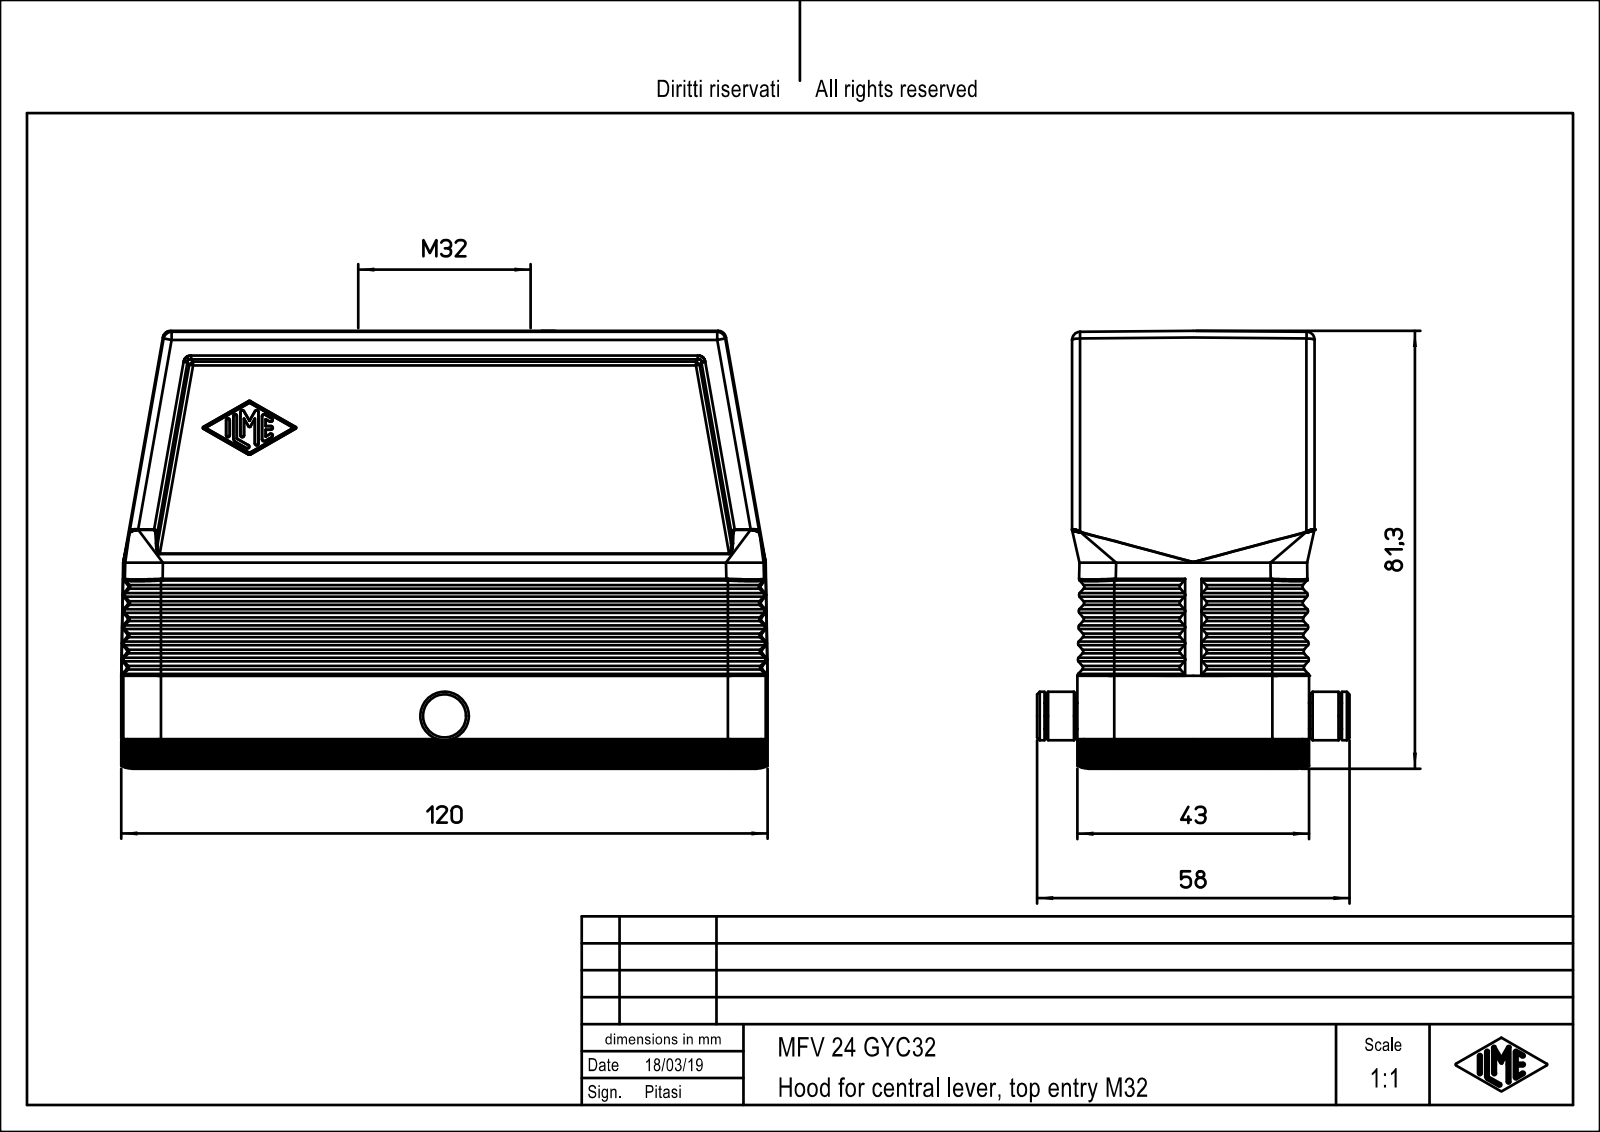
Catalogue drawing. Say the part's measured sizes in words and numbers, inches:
The part is named "MFV_24_GYC32". Its 3-D file was written by "PTC Creo Elements/Direct Modeling 19.0E 27-Jun-2016 (C) Parametric Technology GmbH (AUTOMOTIVE_DESIGN)". It is 1 solid with 574 faces: 224 planar, 182 cylindrical and 168 other. Overall it measures 4.724 by 3.199 by 2.283 inches. Its volume is 7.583 cubic inches and its surface area 90.57 square inches. Round holes: 4 of diameter 0.118, 1 of diameter 1.26. Round bosses or shafts: 1 of diameter 0.354, 1 of diameter 0.189. Partial cylindrical surfaces (rounded edges, fillets, slot ends): 84 of radius 0.02, 16 of radius 0.039, 12 of radius 0.276, 10 of radius 0.059, 8 of radius 0.118, 4 of radius 0.138, 4 of radius 0.157, 4 of radius 0.165. The main face-to-face distances are 1.693, 0.039, 0.157, 0.079, 0.237, 1.535, 0.158, 0.315, 1.732, 0.197. The hole center spacings are 1.063, 2.115, 2.115, 4.094, 4.23.
